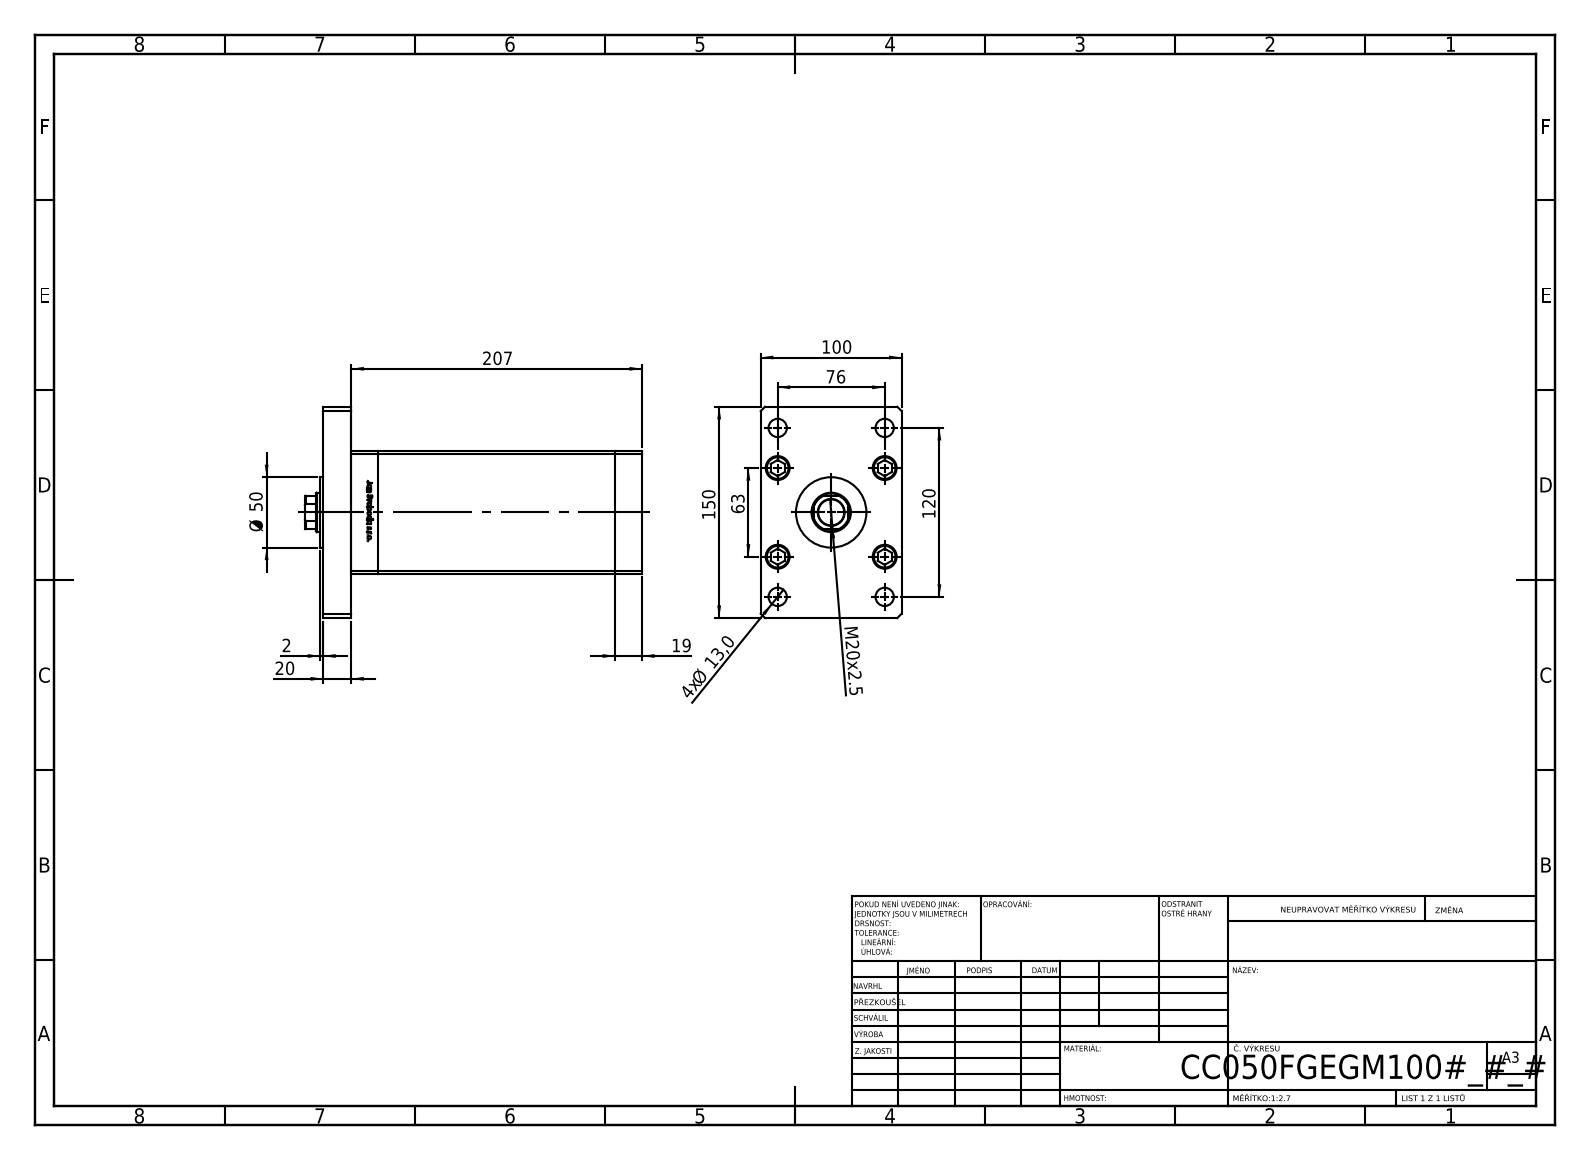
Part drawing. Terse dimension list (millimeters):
name: V220C BACK_F; ALLEN BOLT; V220C_F_MIDDLE; V220C_F (+2 more)
written by: SolidWorks 2019 (CONFIG_CONTROL_DESIGN)
unit: mm
bodies: 19 solids, 1311 faces (517 planar, 188 cylindrical, 606 other)
size: 239.5 × 150 × 100
volume: 1 848 000 mm³; area: 272 154 mm²
holes: 7× ⌀13.5, 7× ⌀18, 4× ⌀12, 4× ⌀13, 4× ⌀17, 2× ⌀2, 2× ⌀13.16, 1× ⌀18.5, 1× ⌀28, 1× ⌀29.5
bosses: 9× ⌀8, 5× ⌀17, 1× ⌀50
rounds: 2× R0.93, 1× R13.5
face distances: 100, 19, 187.5, 87, 20, 168.5, 207.5, 39, 206.5, 226.5
hole spacings: 34, 18.59, 28.5, 37.13, 39.64, 49.36, 57.95, 71.02
